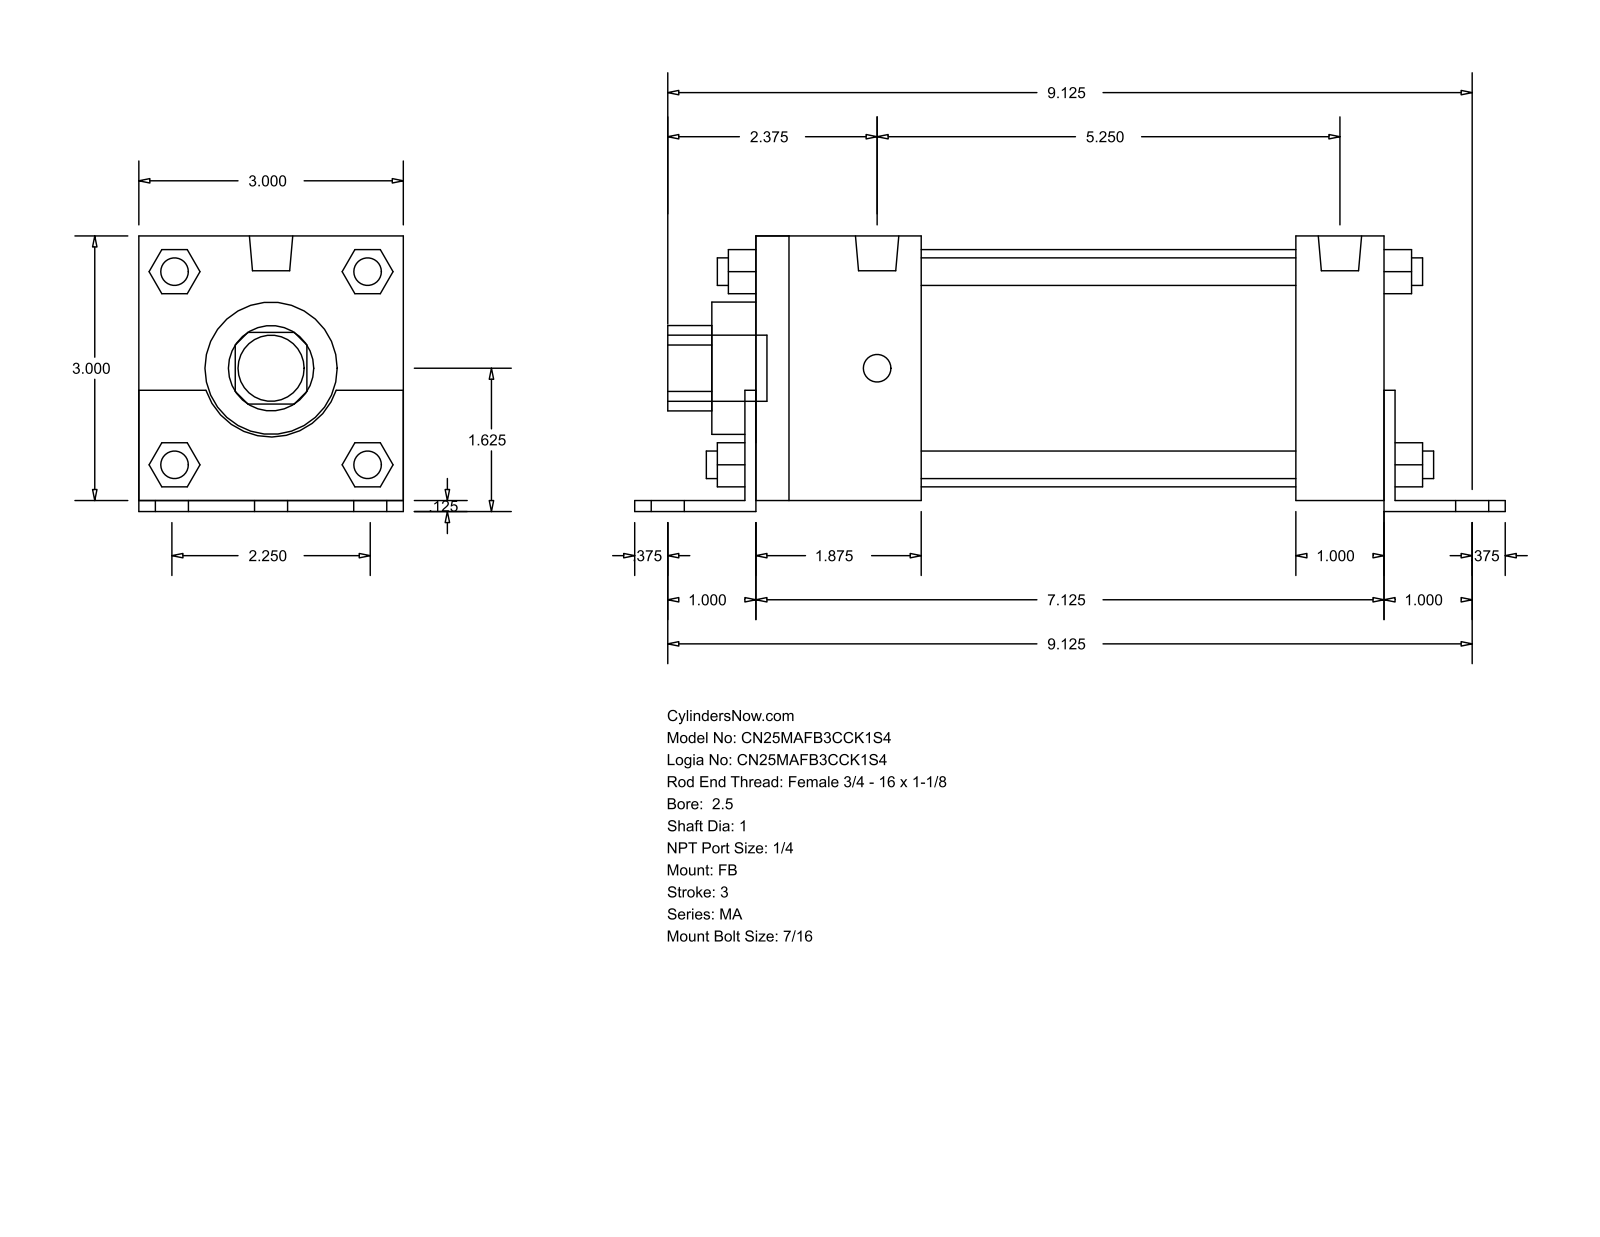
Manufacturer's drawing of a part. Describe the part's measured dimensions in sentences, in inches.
The part is named "MA_FB__0250_1". Its 3-D file was written by "GSSL Pune (CONFIG_CONTROL_DESIGN)". It is 0 solids with 140 faces: 105 planar, 35 cylindrical and 0 other. Overall it measures 9.875 by 3.125 by 3 inches. Round holes: 1 of diameter 1, 1 of diameter 1.5, 1 of diameter 2.69. Round bosses or shafts: 8 of diameter 0.313, 6 of diameter 0.437, 2 of diameter 0.492, 1 of diameter 0.75. Partial cylindrical surfaces (rounded edges, fillets, slot ends): 1 of radius 0.484, 1 of radius 0.78. The main face-to-face distances are 3, 0.125, 3.125, 7.25, 7.125, 0.5, 1.875, 5.25, 5.375, 6.125.
